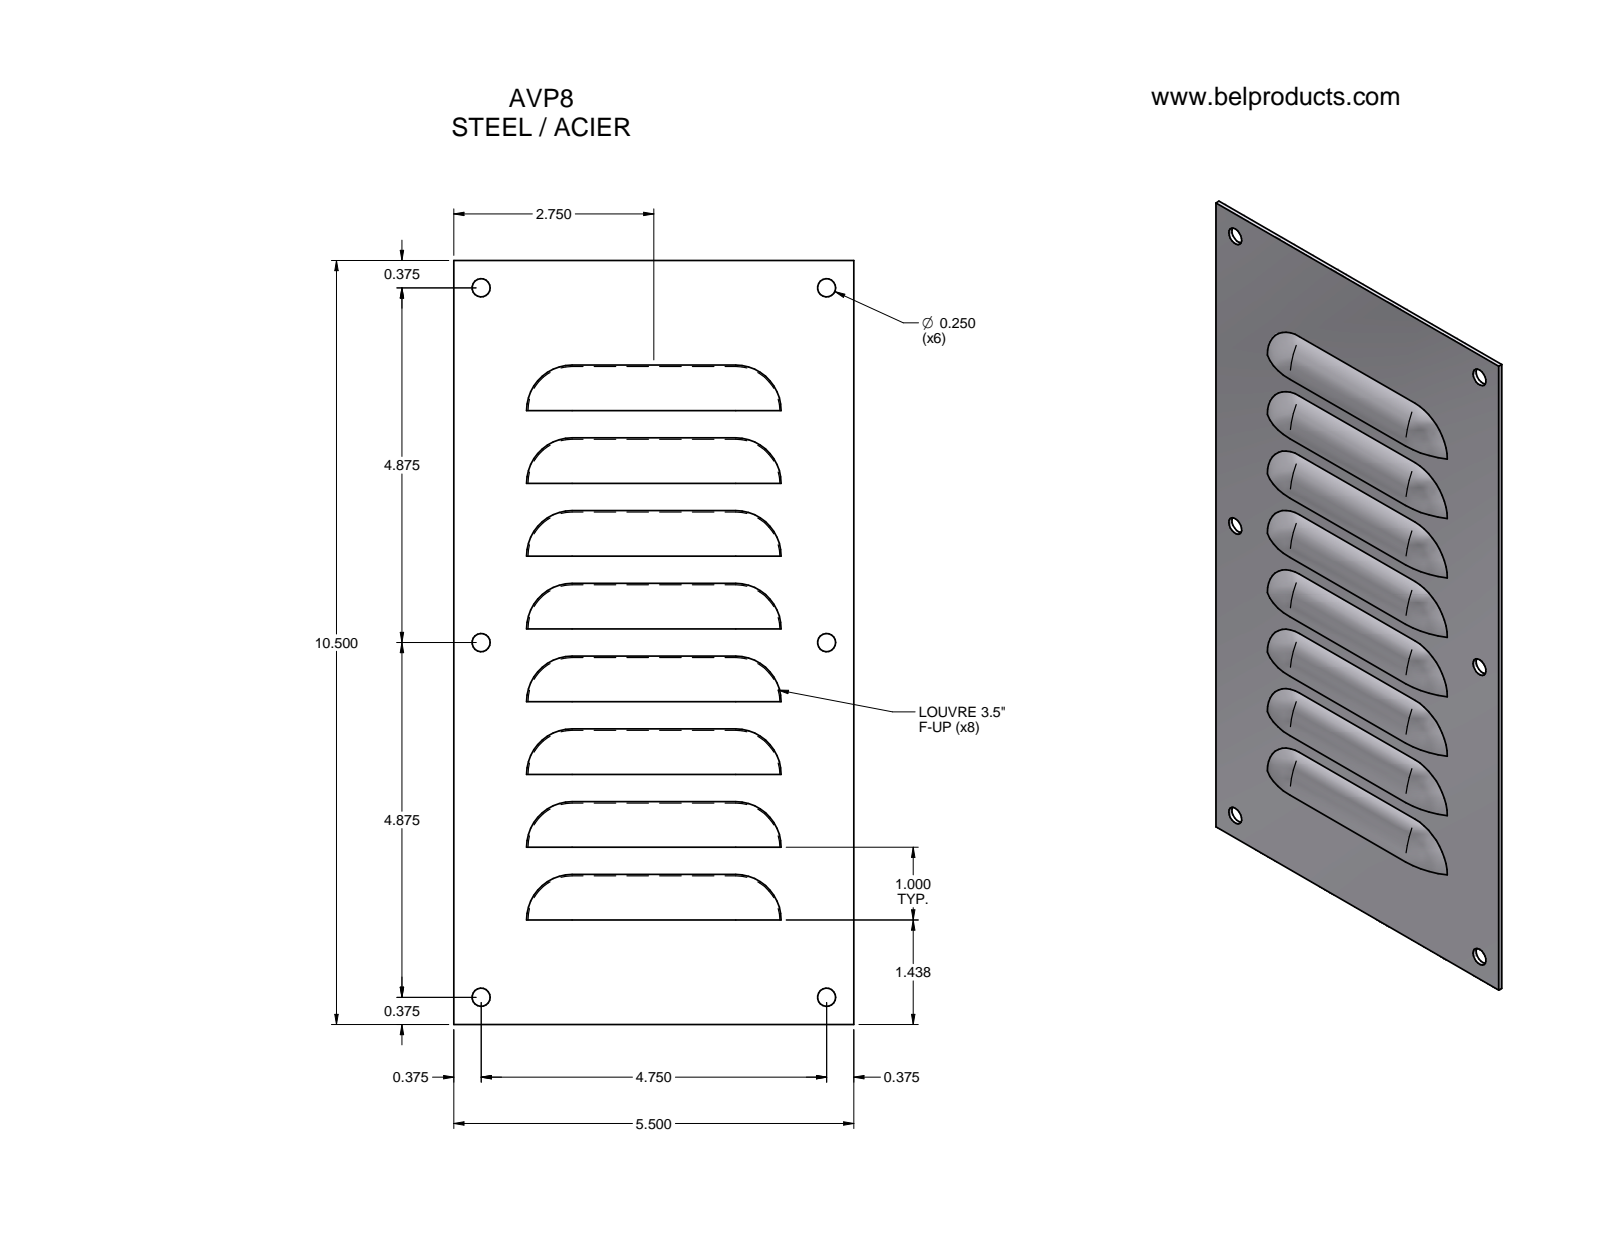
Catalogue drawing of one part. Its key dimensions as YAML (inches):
step_written_by: "Unknown (AUTOMOTIVE_DESIGN)"
units: inches
bodies: {solids: 1, faces: 76, planar: 22, cylindrical: 22, other: 32}
overall_size: [10.5, 5.5, 0.247]
volume: 3.514
surface_area: 122.6
round_holes:
  - {diameter: 0.25, count: 6}
partial_cylinders:
  - {radius: 1.078, count: 8}
  - {radius: 1.138, count: 8}
face_to_face_distances: [0.06, 1, 2, 3, 4, 5, 6, 5.5, 7, 1.438]
hole_center_spacings: [4.875, 6.807, 4.75, 9.75, 10.846]
